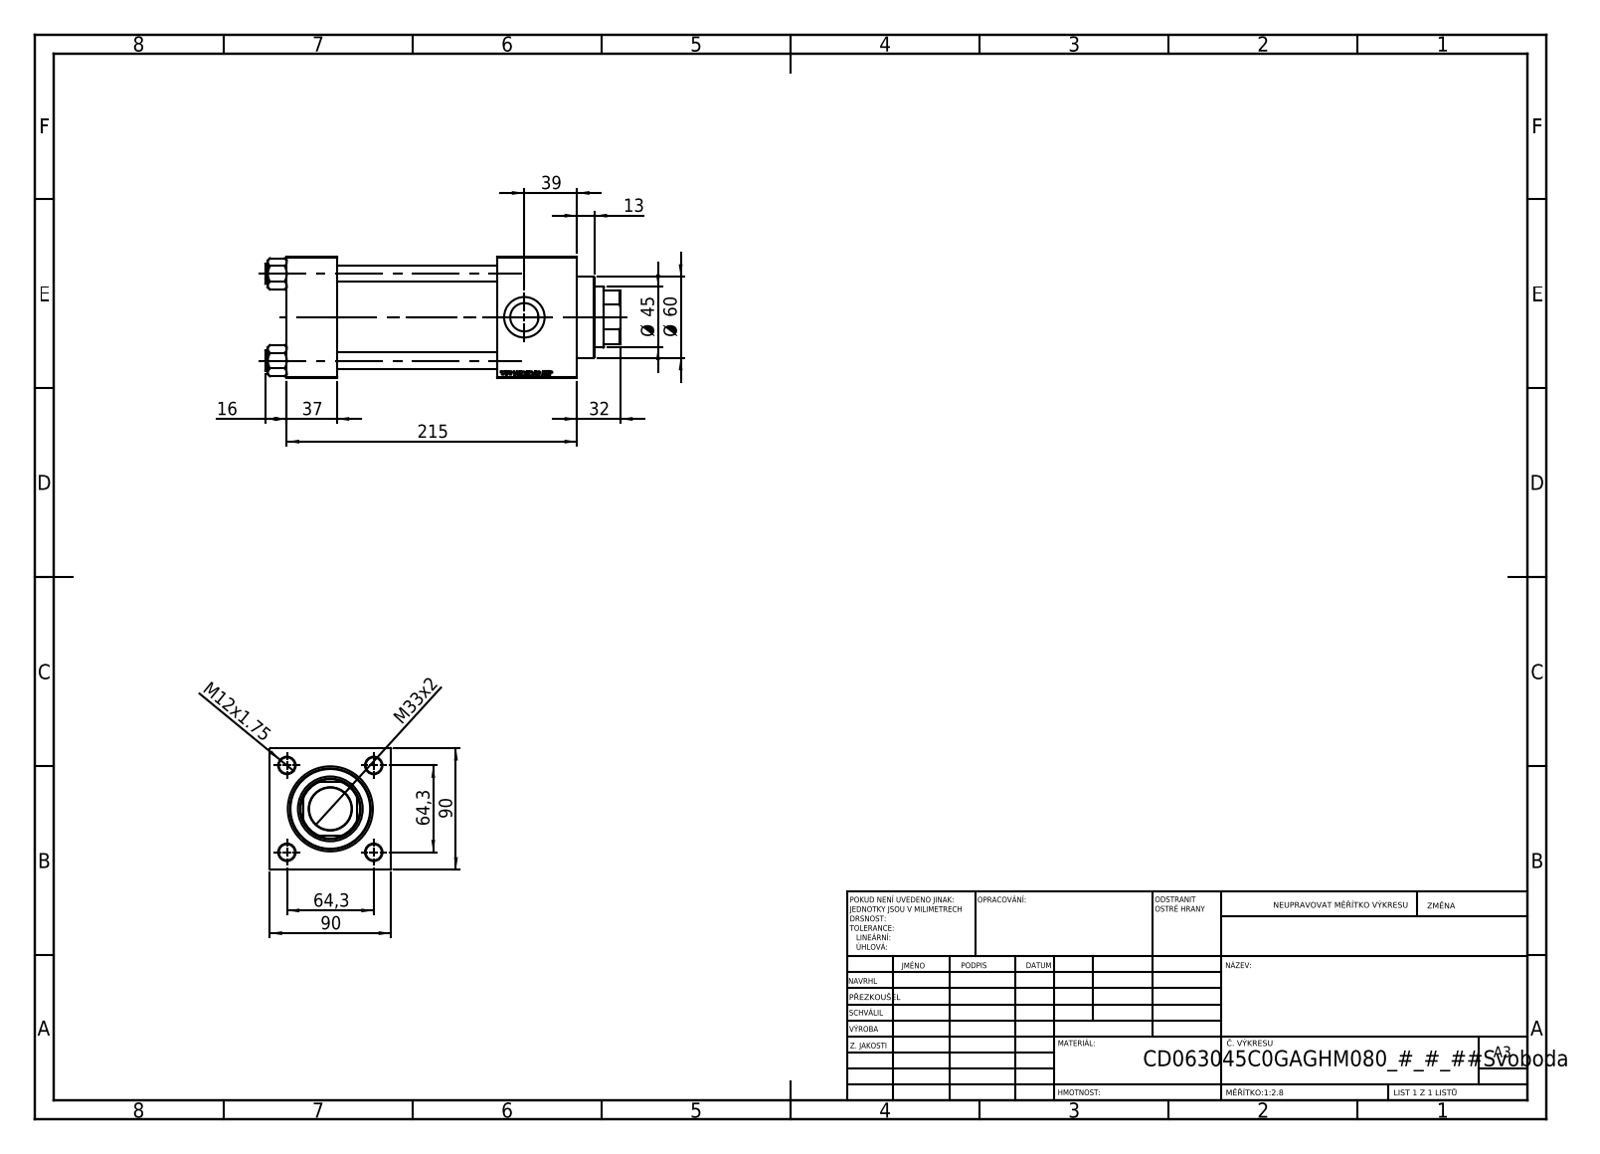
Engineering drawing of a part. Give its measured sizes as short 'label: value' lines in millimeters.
name: V215CD_C_TYCINKA; NUT_M5_V215CD_C; V215CD_Body_C; V215CD_VCP_C (+1 more)
written by: SolidWorks 2019 (CONFIG_CONTROL_DESIGN)
unit: mm
bodies: 11 solids, 1146 faces (525 planar, 85 cylindrical, 536 other)
size: 263 × 90 × 90
volume: 1 158 000 mm³; area: 232 347 mm²
holes: 4× ⌀12, 2× ⌀7, 2× ⌀20.96, 2× ⌀30, 1× ⌀31.5, 1× ⌀45, 1× ⌀48, 1× ⌀50, 1× ⌀60, 1× ⌀63
bosses: 4× ⌀15, 1× ⌀69
rounds: 1× R22
face distances: 90, 37, 59, 156, 119, 215, 178, 186.3, 149.3, 30.3
hole spacings: 45.47, 64.3, 90.93
